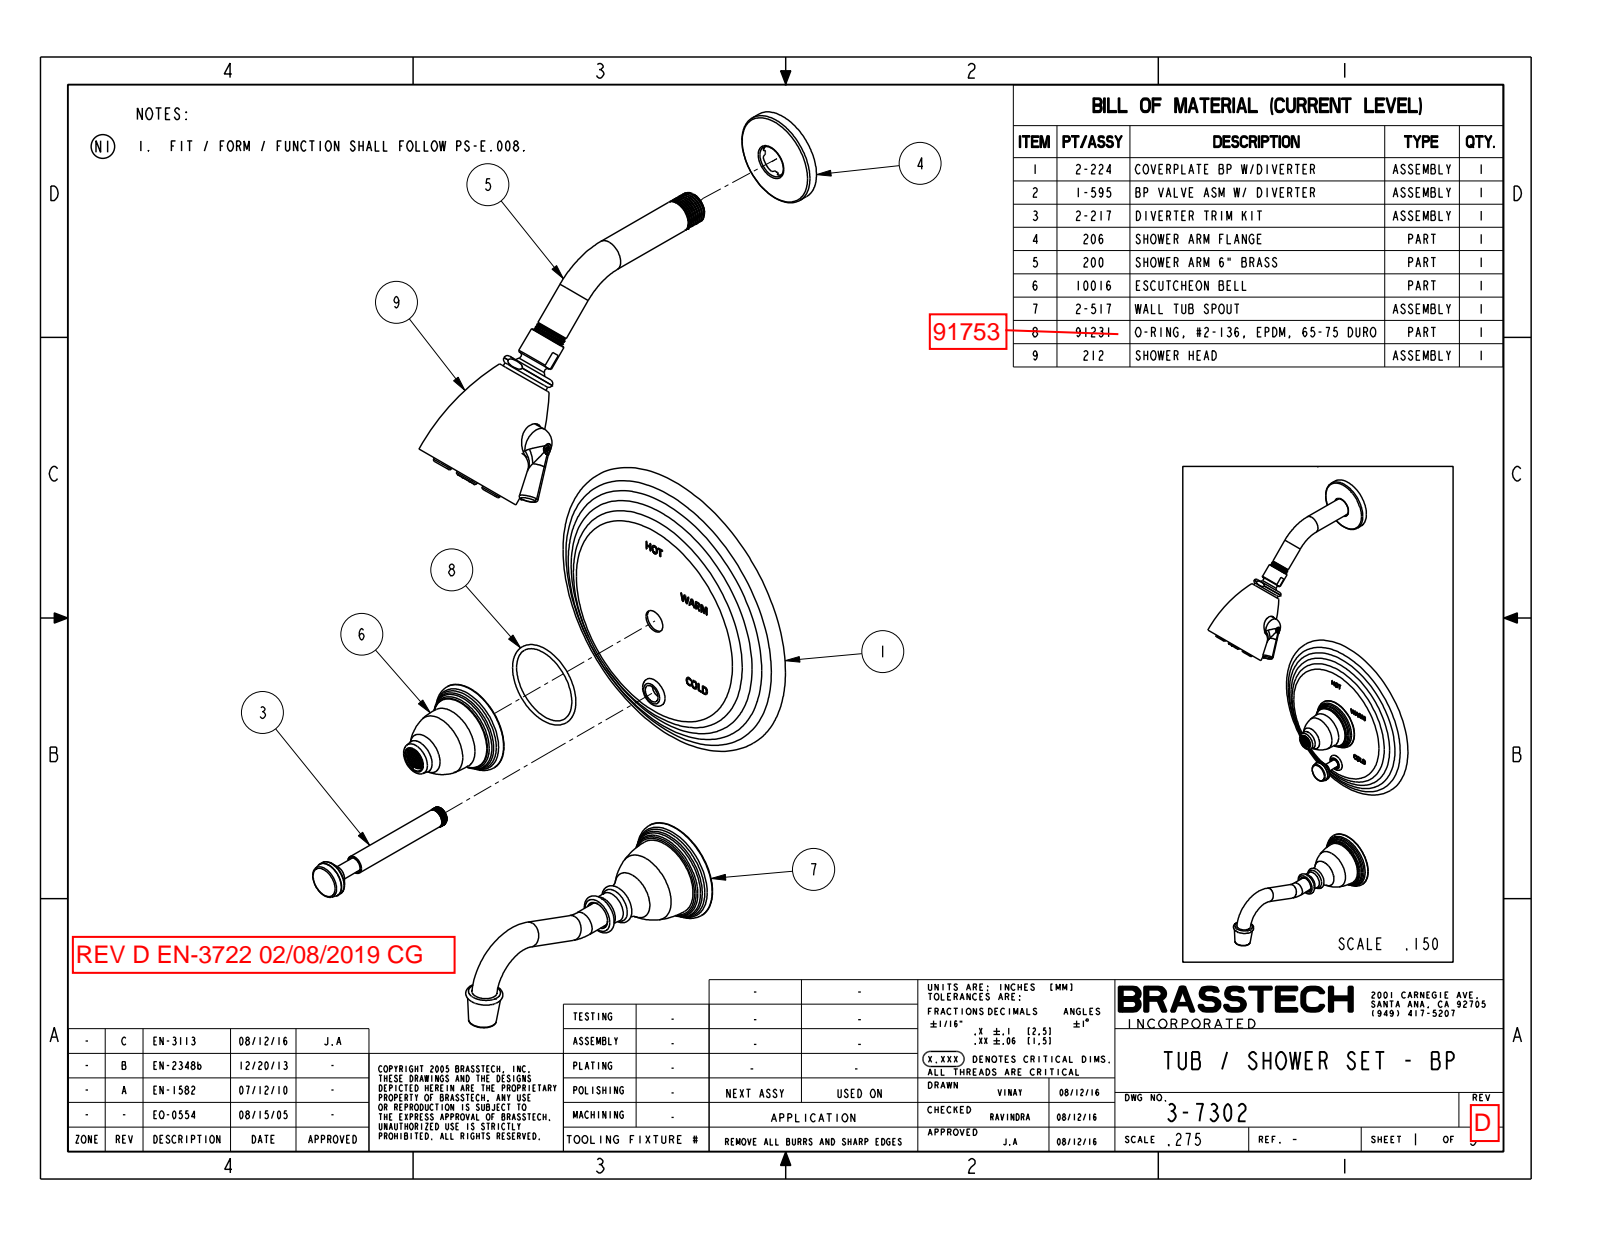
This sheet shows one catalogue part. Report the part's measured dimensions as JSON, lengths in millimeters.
{"part_name": "3-7302_SW0001", "step_written_by": "PRO/ENGINEER BY PARAMETRIC TECHNOLOGY CORPORATION, 2009300 (CONFIG_CONTROL_DESIGN)", "units": "millimeters", "bodies": {"solids": 0, "faces": 801, "planar": 201, "cylindrical": 296, "other": 304}, "overall_size": [571.2, 269.3, 196.9], "round_holes": [[12.7, 3], [17.4, 2], [4.7, 1], [6, 1], [10, 1], [10.9, 1], [11.2, 1], [12.9, 1], [14.2, 1], [14.3, 1], [15.1, 1], [15.2, 1]], "round_bosses_or_shafts": [[2.5, 6], [20.7, 2], [19.5, 2], [15.9, 2], [66, 1], [60.5, 1], [31, 1], [22.9, 1]], "partial_cylinders_radius": [[0.8, 3], [2.9, 1], [11.9, 1], [17.5, 1]], "face_to_face_distances": [1.3, 17.9, 19.2, 2.5, 53.5, 35.6, 34.4, 15.2, 80.2, 77.6], "hole_center_spacings": [55, 148.2, 203.2, 304.8, 359.8, 508]}
